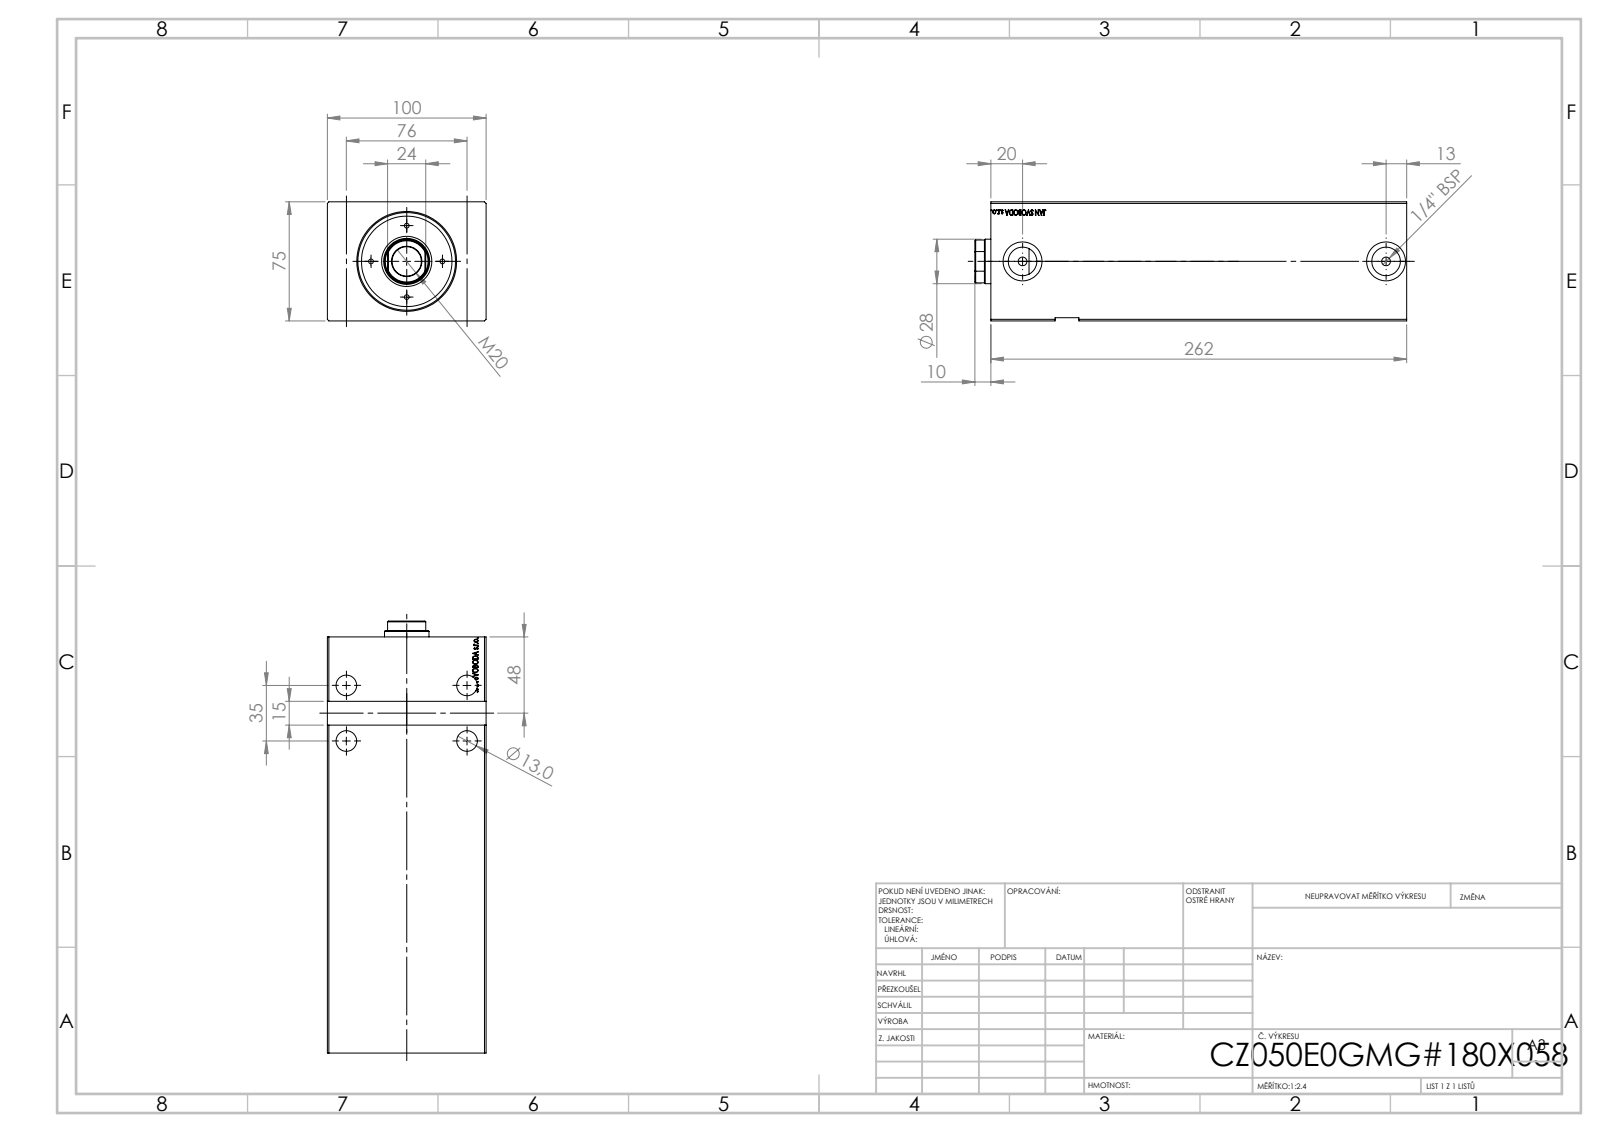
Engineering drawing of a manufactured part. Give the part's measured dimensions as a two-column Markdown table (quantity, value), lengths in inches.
| quantity | value |
| --- | --- |
| STEP written by | SolidWorks 2019 (CONFIG_CONTROL_DESIGN) |
| units | inches |
| bodies | 1 solid, 775 faces (375 planar, 30 cylindrical, 370 other) |
| overall size | 10.315 × 3.937 × 2.953 |
| volume | 86.96 in³ |
| surface area | 244.8 in² |
| round holes (diameter × count) | 0.512 × 4, 0.217 × 2, 0.315 × 2, 0.709 × 2, 0.965 × 2, 1.417 × 1, 1.969 × 1, 2.421 × 1 |
| main face-to-face distances | 2.953, 3.937, 10.315, 9.614, 0.701, 0.079, 2.874, 10.307, 0.693, 0.394 |
| hole center spacings | 1.378, 2.992, 3.294, 0.828, 1.371, 2.22, 2.474, 6.641 |
